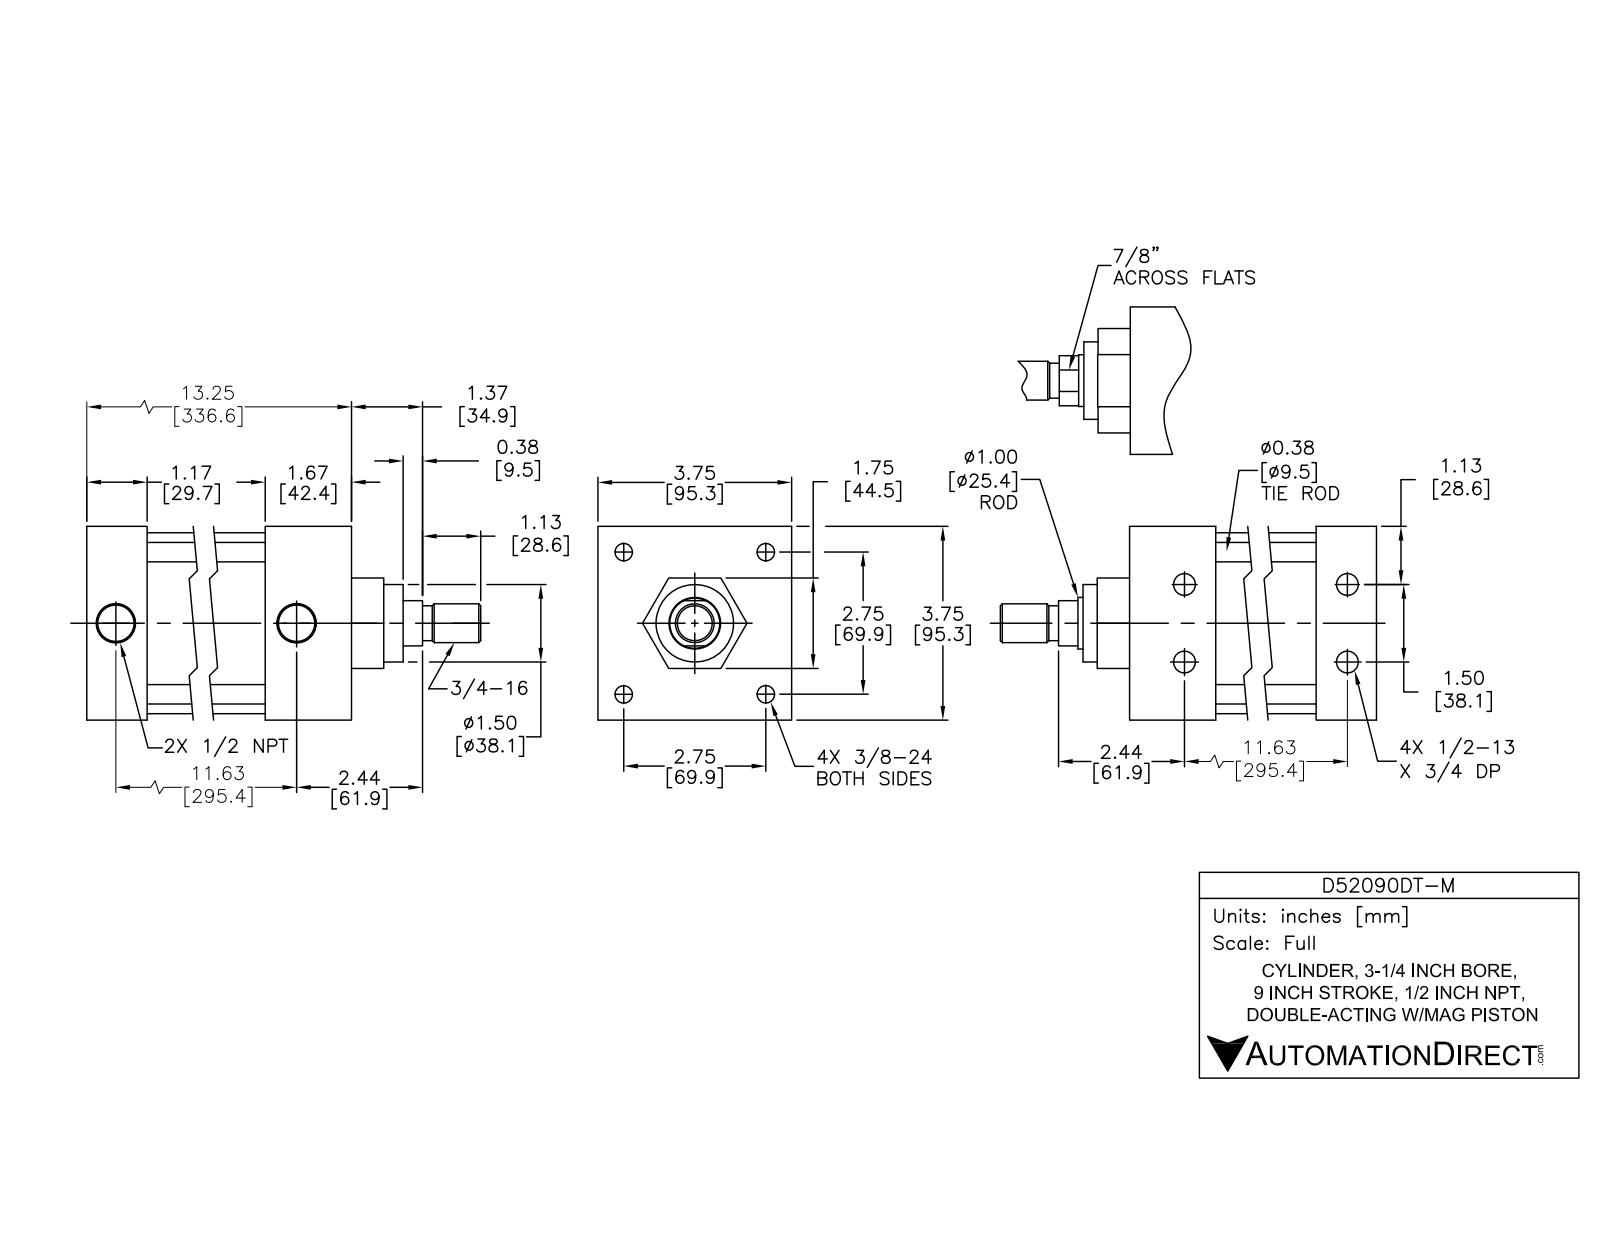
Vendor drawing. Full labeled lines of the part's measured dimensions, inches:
Part name (STEP PRODUCT): D52090DT-M PISTON; D52090DT-M; D52090DT-M BODY
STEP written by: SolidWorks 2015 (AUTOMOTIVE_DESIGN)
Units: inches
Bodies: 12 solids, 303 faces (99 planar, 114 cylindrical, 90 other)
Overall size (bounding box): 15.745 × 3.75 × 3.75
Volume: 76.05 in³ · Surface area: 494.6 in²
Round holes (diameter × count): ⌀0.33 ×4, ⌀0.406 ×4, ⌀0.417 ×4, ⌀0.625 ×4, ⌀0.5 ×2, ⌀0.766 ×2, ⌀1 ×1, ⌀1.003 ×1, ⌀3.25 ×1
Round bosses / shafts (diameter × count): ⌀0.609 ×4, ⌀0.375 ×4, ⌀0.34 ×4, ⌀3.5 ×1, ⌀3.247 ×1, ⌀1.75 ×1, ⌀0.997 ×1, ⌀0.97 ×1
Partial cylindrical surfaces — rounded edges, fillets, slot ends (radius × count): R0.375 ×4
Main face-to-face distances: 3.75, 0.08, 10.326, 13.246, 1.75, 11.997, 1.249, 10.751, 1.246, 2.495
Hole centre spacings: 2.758, 1.95, 0.75, 0.76, 1.5, 3.9, 11.5, 11.528
